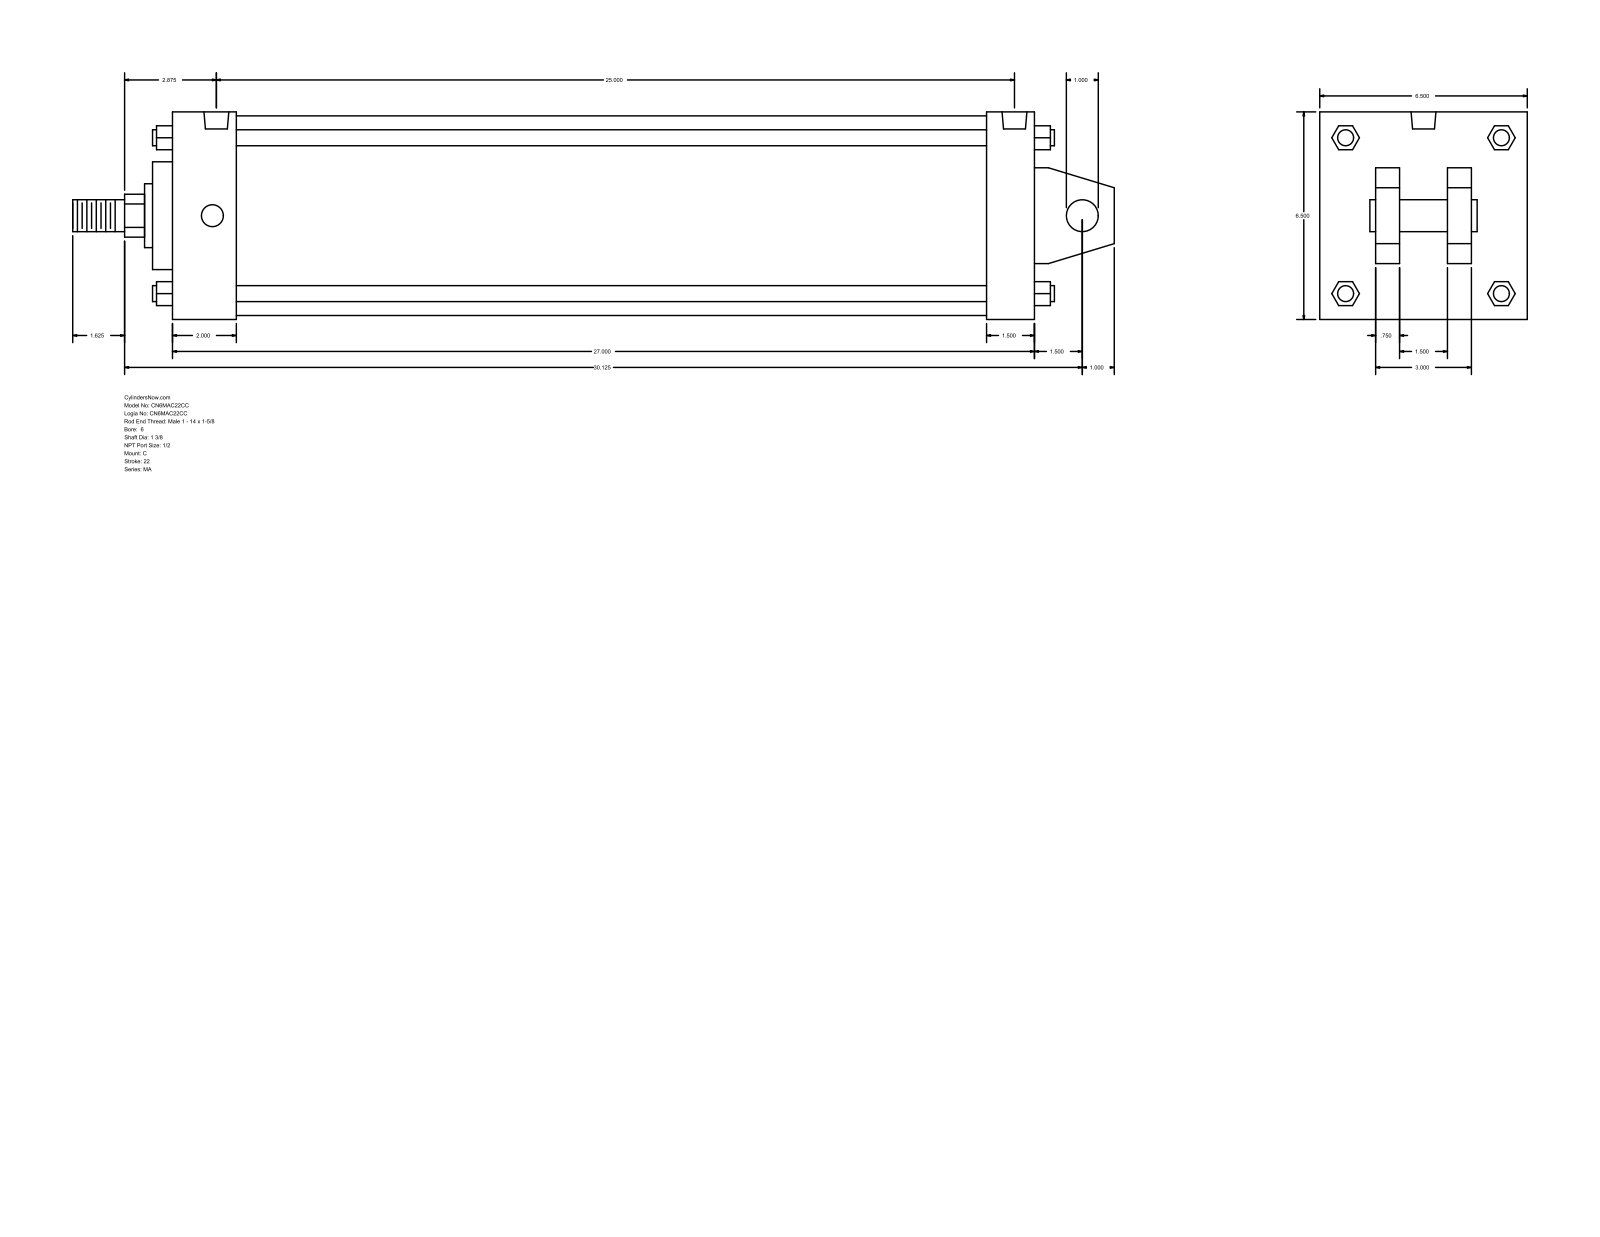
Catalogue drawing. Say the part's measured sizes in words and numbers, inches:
The part is named "MA_C__0600_1.375". Its 3-D file was written by "GSSL Pune (CONFIG_CONTROL_DESIGN)". It is 0 solids with 141 faces: 109 planar, 32 cylindrical and 0 other. Overall it measures 32.625 by 6.5 by 6.5 inches. Round holes: 4 of diameter 0.687, 2 of diameter 0.778. Round bosses or shafts: 4 of diameter 0.5, 2 of diameter 1, 1 of diameter 6.25, 1 of diameter 3.375, 1 of diameter 2, 1 of diameter 1.375. Partial cylindrical surfaces (rounded edges, fillets, slot ends): 1 of radius 0.672. The main face-to-face distances are 6.5, 27, 1.5, 0.75, 2.5, 4, 2, 1.75, 4.75, 25.5. The hole center spacings are 25, 0.125, 0.125, 24.875, 25, 25.125.
